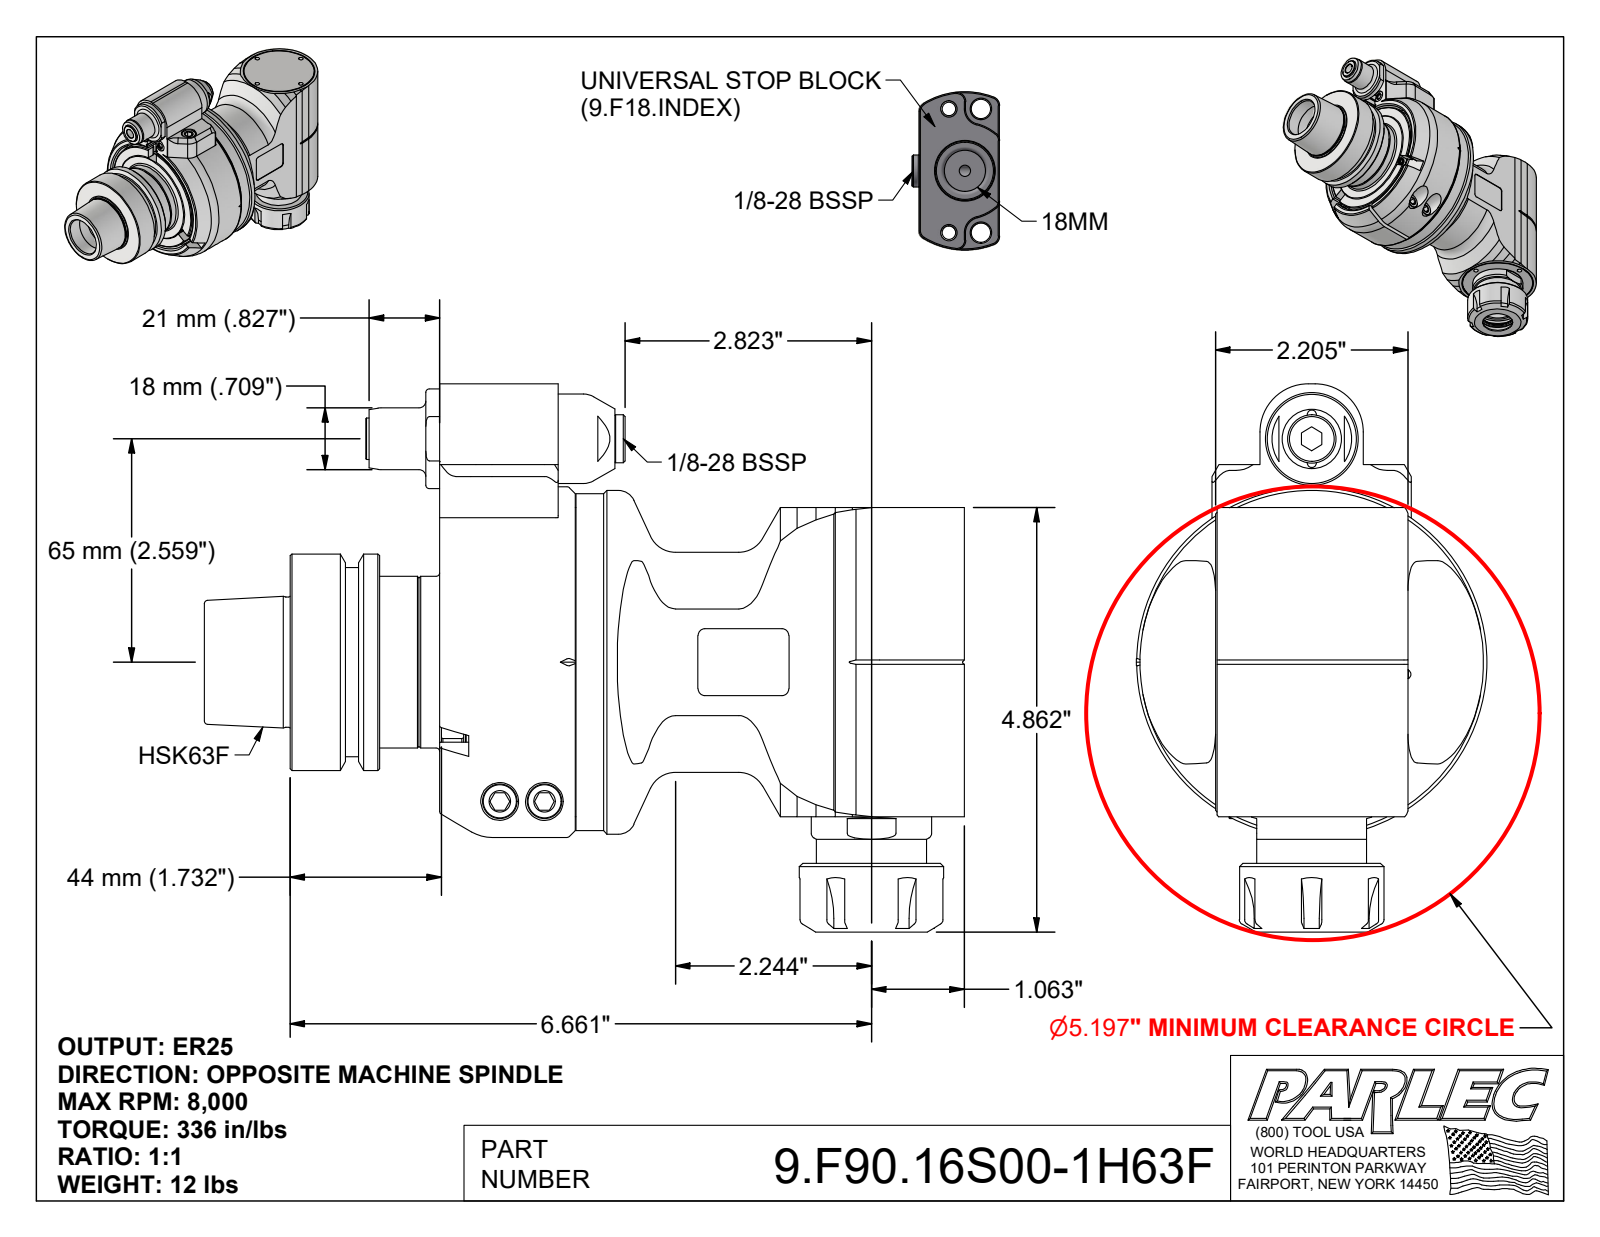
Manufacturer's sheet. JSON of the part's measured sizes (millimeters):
{"part_name": "9.F90.16S00-1H63F; 9_F90_16S00; 9GA11C_C66 (EVO, Type 1, HSK63F, 65mm)", "step_written_by": "Autodesk Inventor 2022 (AUTOMOTIVE_DESIGN)", "units": "millimeters", "bodies": {"solids": 4, "faces": 617, "planar": 276, "cylindrical": 156, "other": 185}, "overall_size": [221.2, 159.5, 102], "volume_mm3": 978600, "surface_area_mm2": 140400, "round_holes": [[3.2, 4], [6.5, 3], [2.6, 2], [3.3, 2], [4.2, 2], [5, 2], [8, 2], [10.4, 2], [11, 2], [12.5, 2], [27, 2], [2.5, 1]], "round_bosses_or_shafts": [[10, 4], [18, 2], [12, 2], [8, 2], [6, 2], [2.5, 2], [102, 1], [100, 1]], "partial_cylinders_radius": [[1, 14], [2, 12], [3, 6], [25, 6], [4, 4], [0.4, 2], [0.5, 2], [8, 2]], "face_to_face_distances": [32, 26, 0.5, 31.8, 7, 8.5, 1, 52, 25, 56], "hole_center_spacings": [21.5, 30.4, 7, 12.8, 18.8, 25.3, 43, 48.7]}
